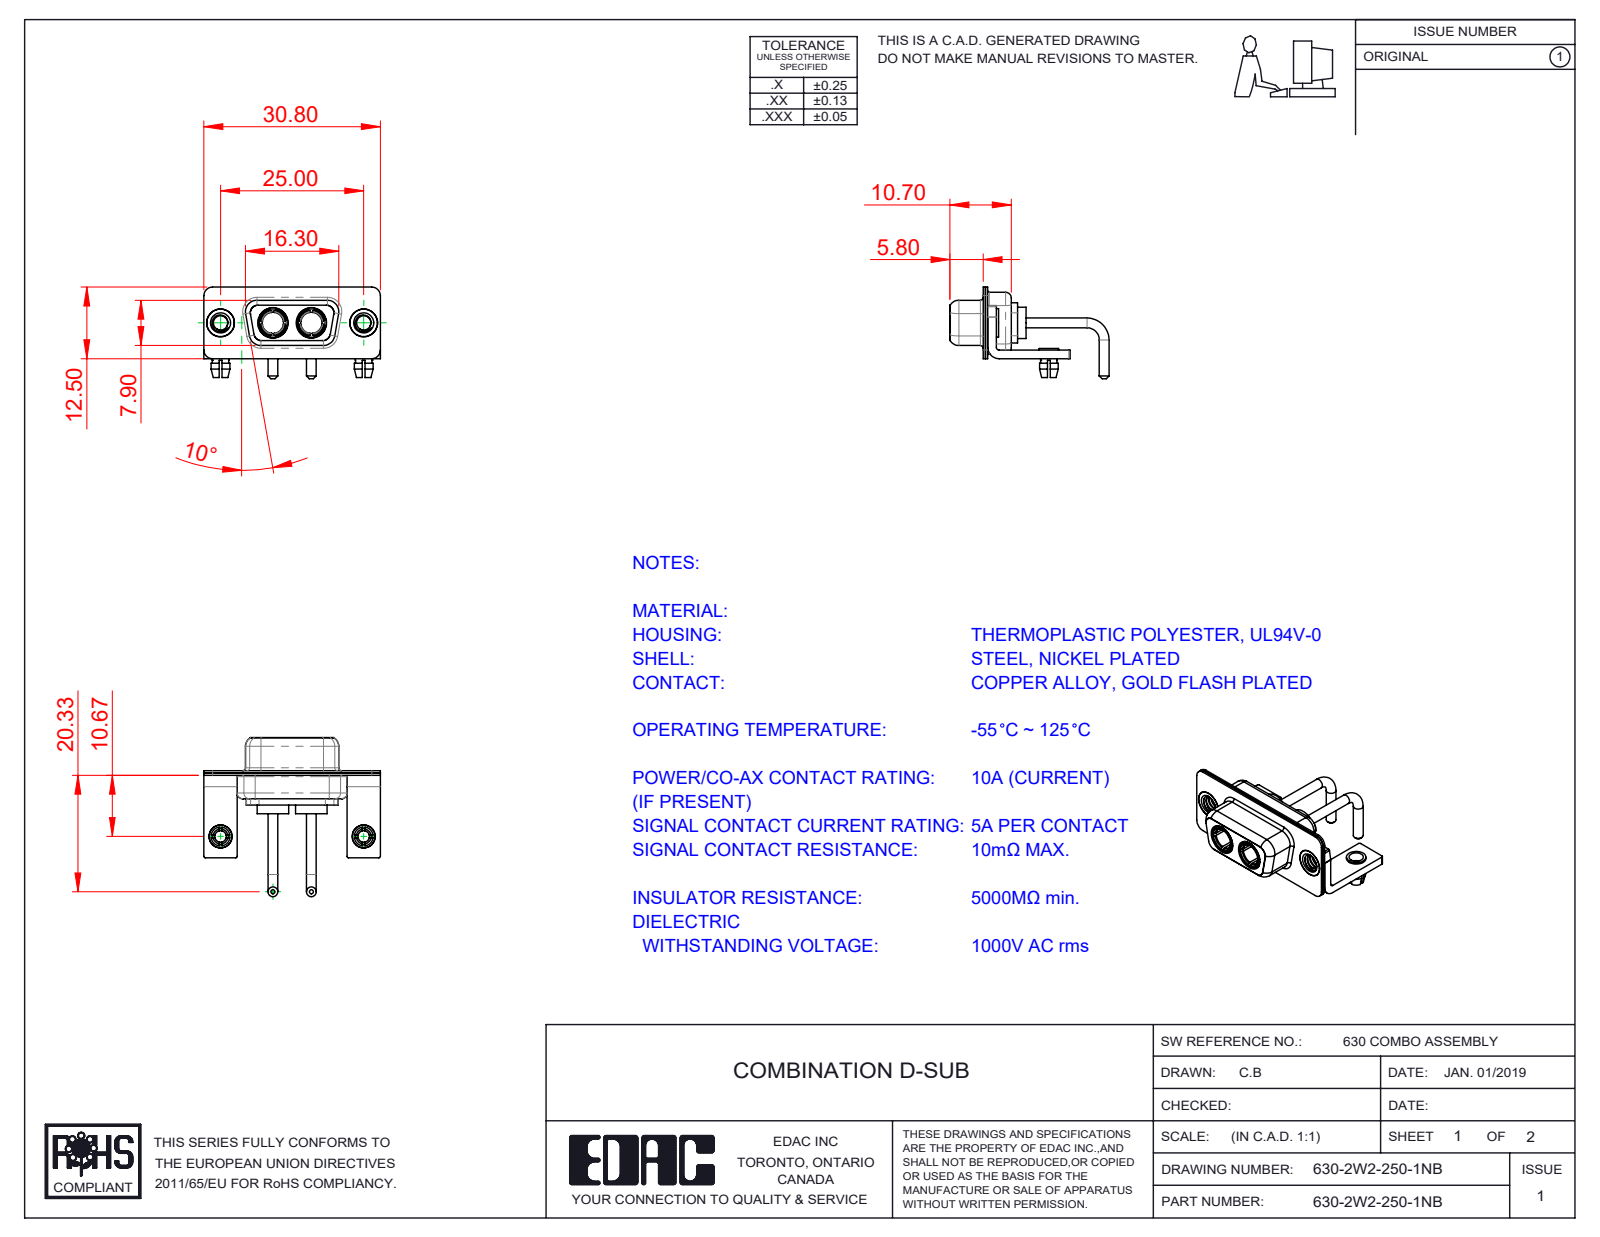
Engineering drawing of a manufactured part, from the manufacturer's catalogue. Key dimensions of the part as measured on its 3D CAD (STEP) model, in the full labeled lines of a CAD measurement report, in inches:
Part name (STEP PRODUCT): Power Socket_Ext 10A RA; 630Combo Threaded Rivet_B; 630Combo Shell Front_09 Contacts; 630-2W2-250-1NB (+4 more)
STEP written by: SolidWorks 2020 (CONFIG_CONTROL_DESIGN)
Units: inches
Bodies: 13 solids, 565 faces (193 planar, 237 cylindrical, 135 other)
Overall size (bounding box): 1.213 × 1.094 × 0.63
Volume: 0.123 in³ · Surface area: 8.007 in²
Round holes (diameter × count): ⌀0.098 ×4, ⌀0.191 ×4, ⌀0.079 ×2, ⌀0.126 ×2, ⌀0.146 ×2, ⌀0.157 ×2, ⌀0.159 ×2, ⌀0.209 ×2
Round bosses / shafts (diameter × count): ⌀0.067 ×4, ⌀0.217 ×2, ⌀0.205 ×2, ⌀0.197 ×2, ⌀0.195 ×2, ⌀0.195 ×2, ⌀0.189 ×2, ⌀0.187 ×2
Partial cylindrical surfaces — rounded edges, fillets, slot ends (radius × count): R0.01 ×16, R0.059 ×16, R0.079 ×13, R0.053 ×8, R0.063 ×8, R0.02 ×5, R0.024 ×4, R0.026 ×4
Main face-to-face distances: 0.016, 0.059, 0.031, 0.055, 0.018, 0.333, 0.071, 0.091, 0.35, 0.146
Hole centre spacings: 0.36, 0.624, 0.984, 0.265
